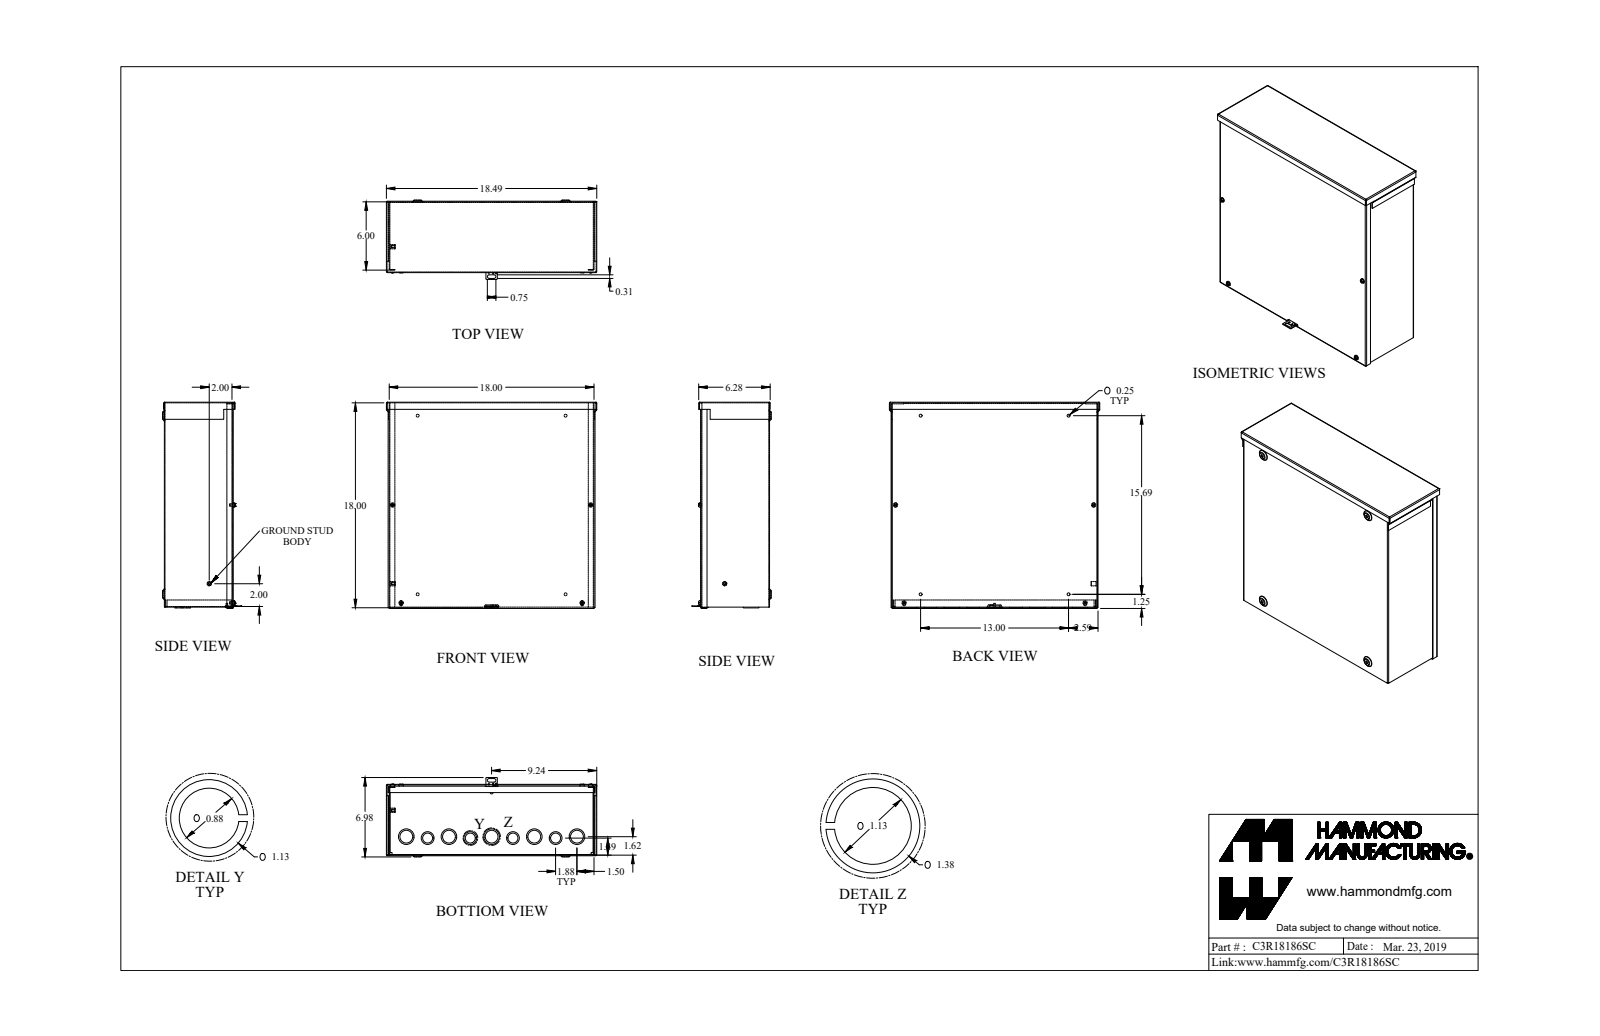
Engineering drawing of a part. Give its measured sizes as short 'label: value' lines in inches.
name: C3R18186SC_Default
written by: SolidWorks 2019 (CONFIG_CONTROL_DESIGN)
unit: in
bodies: 11 solids, 457 faces (238 planar, 133 cylindrical, 86 other)
size: 18.489 × 18.12 × 6.977
volume: 68.47 in³; area: 2 413 in²
holes: 4× ⌀0.17, 4× ⌀0.25, 3× ⌀1.125, 2× ⌀0.875, 2× ⌀0.875, 2× ⌀1.125, 1× ⌀0.125, 1× ⌀0.137, 1× ⌀0.156
bosses: 4× ⌀1.125, 4× ⌀0.19, 3× ⌀1.375, 3× ⌀0.375, 2× ⌀1.375, 2× ⌀0.375, 1× ⌀0.125
rounds: 21× R0.029, 21× R0.086, 8× R0.109, 8× R0.125, 2× R0.156
face distances: 0.057, 6, 5.943, 6.057, 17.943, 18, 0.057, 17.886, 17.886, 17.943
hole spacings: 3.75, 1.879, 1.88, 5.627, 7.5, 8.151, 17.112, 9.376
